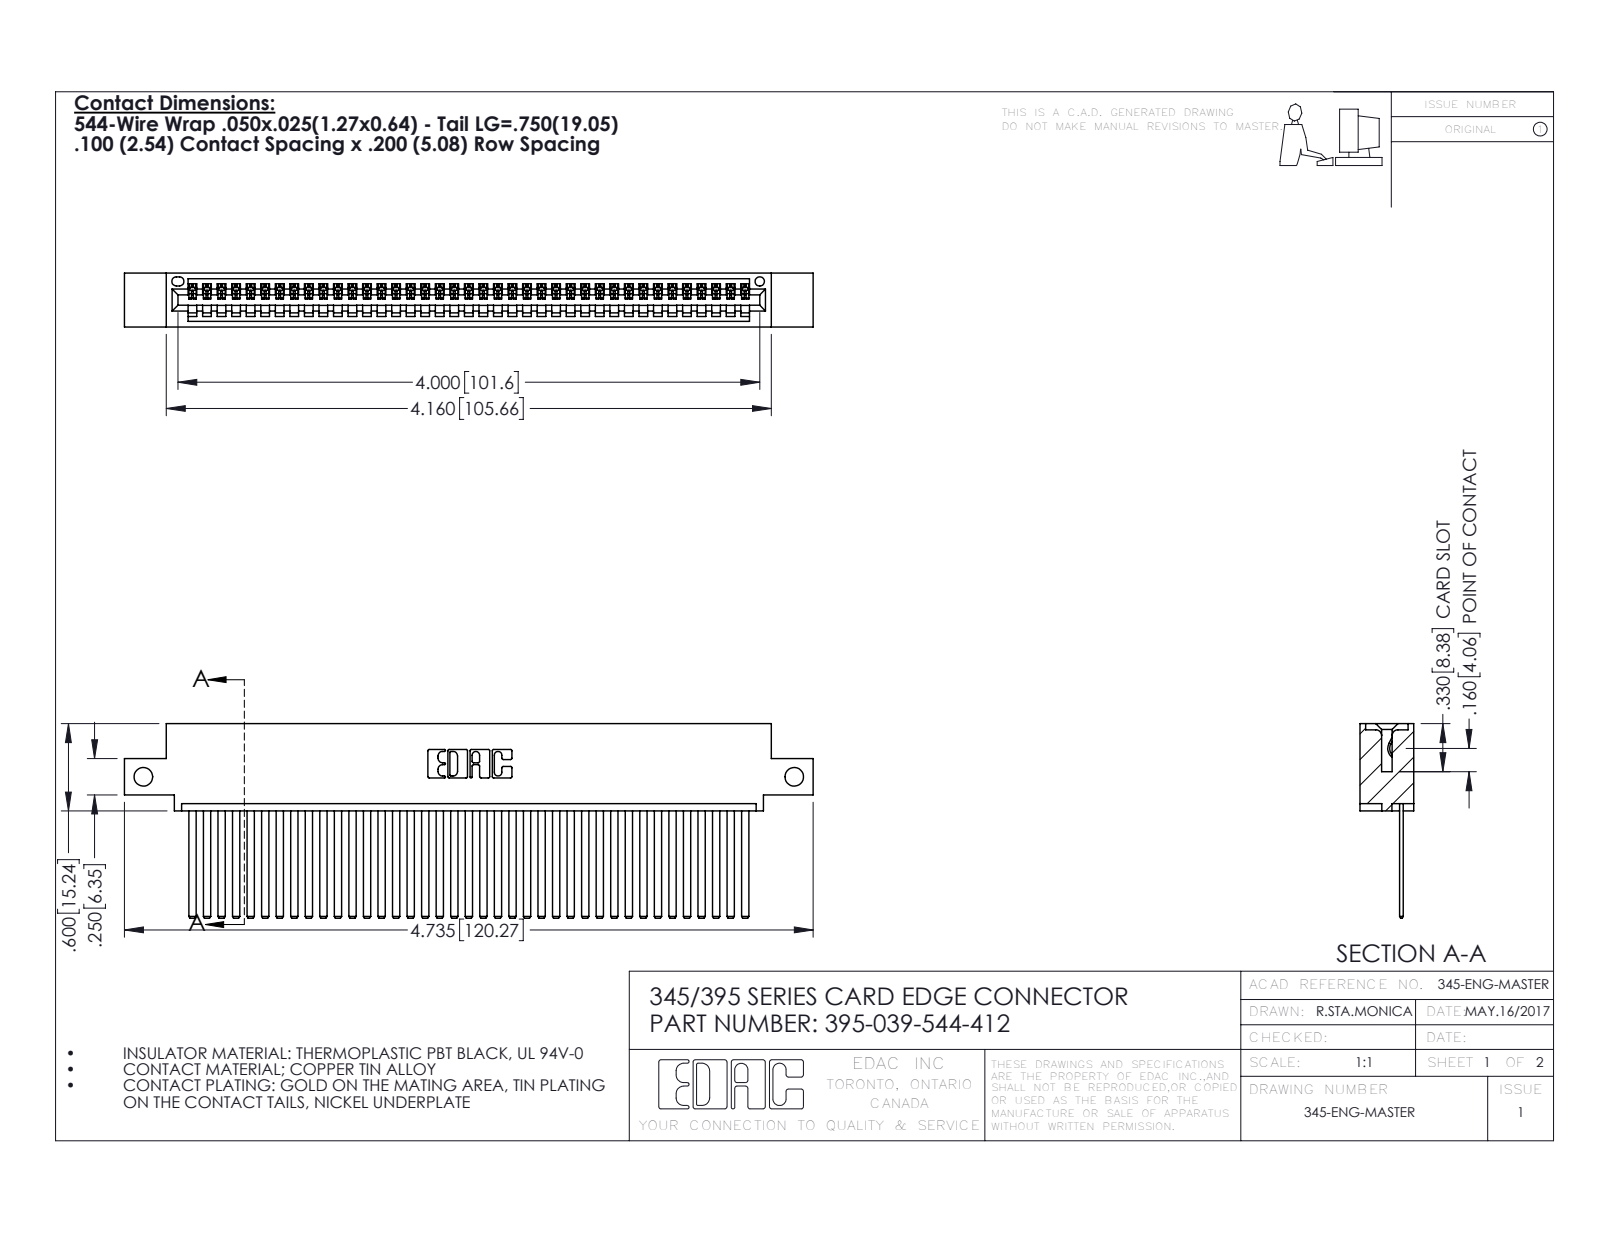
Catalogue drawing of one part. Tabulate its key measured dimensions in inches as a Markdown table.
| quantity | value |
| --- | --- |
| part name | 345 Part_0.110 Offset - Side Mount; 395-039-544-412; 345-292-001_345-293-144 |
| STEP written by | SolidWorks 2016 (CONFIG_CONTROL_DESIGN) |
| units | inches |
| bodies | 40 solids, 2158 faces (1488 planar, 670 cylindrical, 0 other) |
| overall size | 4.735 × 1.337 × 0.37 |
| volume | 0.713 in³ |
| surface area | 26.02 in² |
| round holes (diameter × count) | 0.128 × 2, 0.064 × 1 |
| partial cylindrical surfaces (radius × count) | 0.006 × 78, 0.01 × 22, 0.007 × 6, 0.031 × 6, 0.026 × 3, 0.031 × 2, 0.04 × 2, 0.014 × 1 |
| main face-to-face distances | 0.072, 0.298, 0.025, 0.098, 0.272, 0.37, 0.2, 0.225, 0.149, 0.072 |
| hole center spacings | 4.475 |
